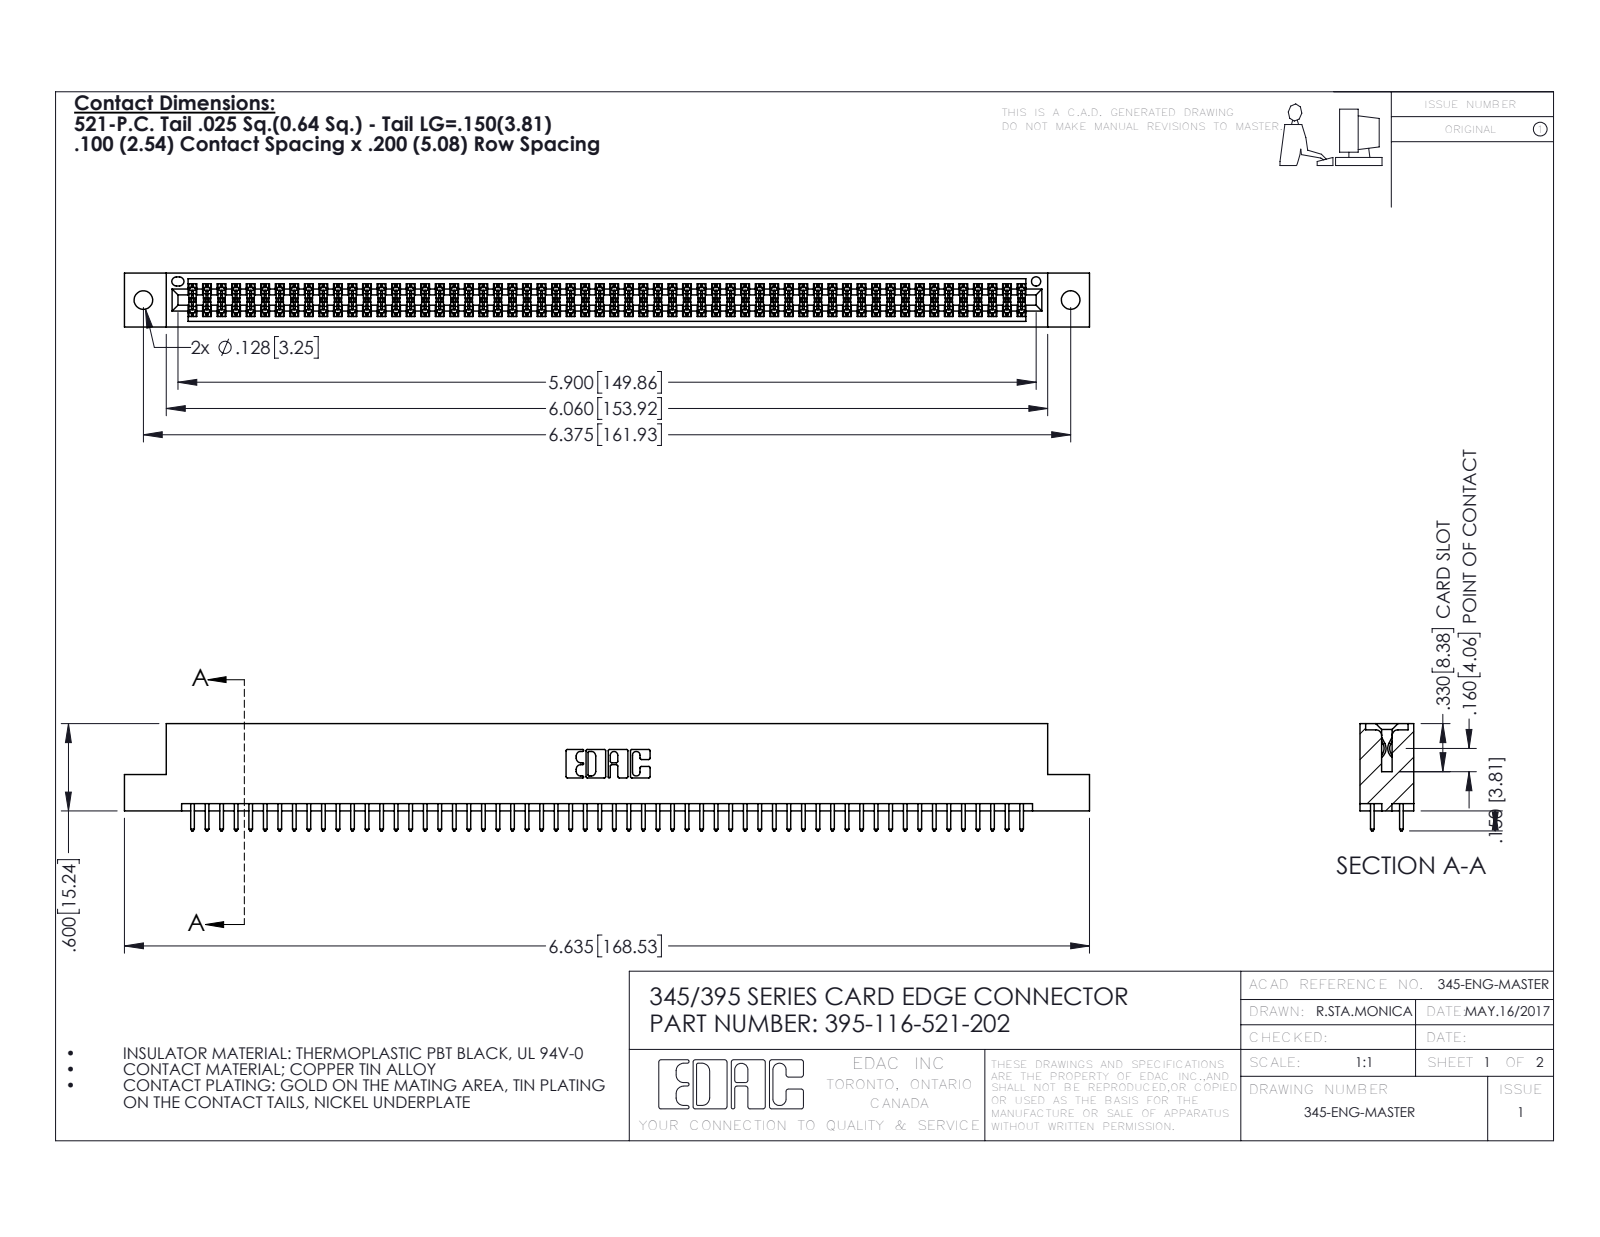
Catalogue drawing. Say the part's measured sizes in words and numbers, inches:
The part is named "345 Part_Flush Mounting Lugs - 0.128 Dia; 395-116-521-202; 345-292-001_345-293-121". Its 3-D file was written by "SolidWorks 2016 (CONFIG_CONTROL_DESIGN)". It is 117 solids with 5926 faces: 3908 planar, 2018 cylindrical and 0 other. Overall it measures 6.635 by 0.737 by 0.37 inches. Its volume is 1.003 cubic inches and its surface area 37.24 square inches. Round holes: 2 of diameter 0.128, 1 of diameter 0.064. Partial cylindrical surfaces (rounded edges, fillets, slot ends): 174 of radius 0.006, 116 of radius 0.01, 22 of radius 0.01, 6 of radius 0.007, 6 of radius 0.031, 3 of radius 0.026, 2 of radius 0.014, 2 of radius 0.019. The main face-to-face distances are 0.298, 0.072, 0.2, 0.098, 0.272, 0.025, 0.37, 0.225, 0.175, 0.149. The hole center spacings are 0.27, 6.139, 6.375.
